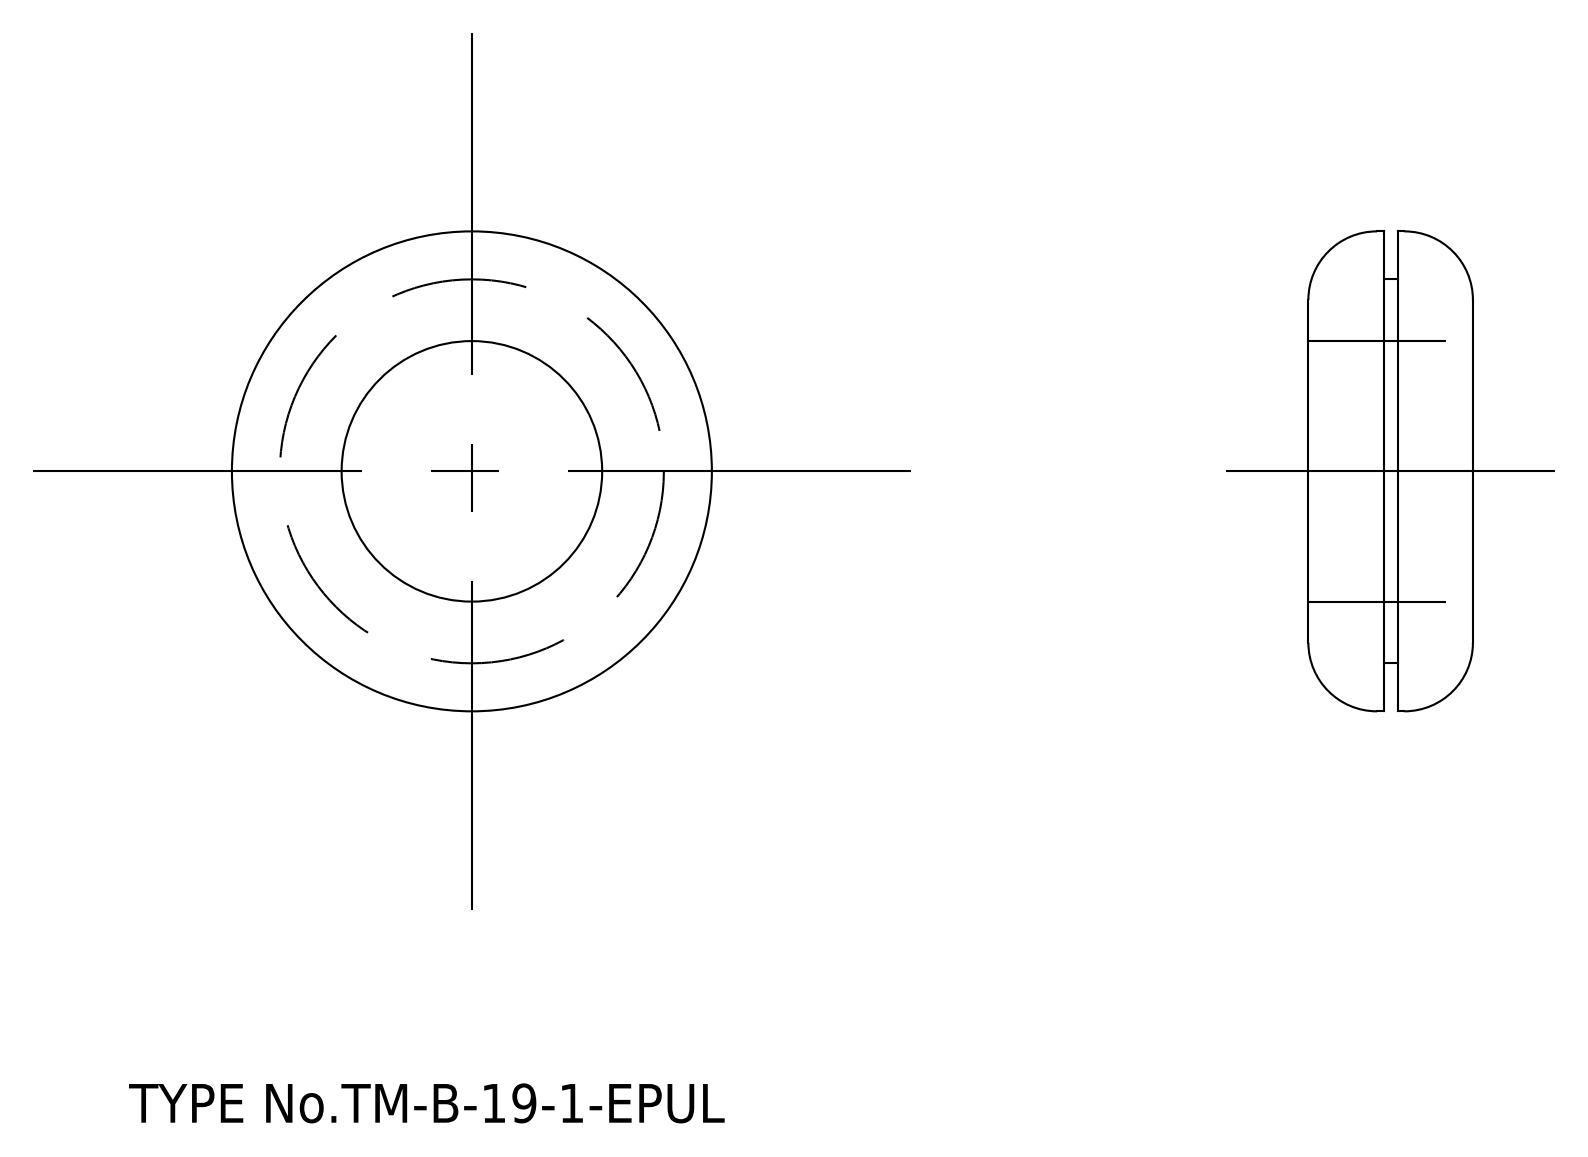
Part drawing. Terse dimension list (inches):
written by: spGate 15.6.1 (AUTOMOTIVE_DESIGN)
unit: in
bodies: 1 solid, 16 faces (4 planar, 8 cylindrical, 4 other)
size: 1.378 × 1.378 × 0.472
volume: 0.409 in³; area: 5.534 in²
holes: 1× ⌀0.748
bosses: 1× ⌀1.378, 1× ⌀1.102
face distances: 0.217, 0.256, 0.039, 0.472
